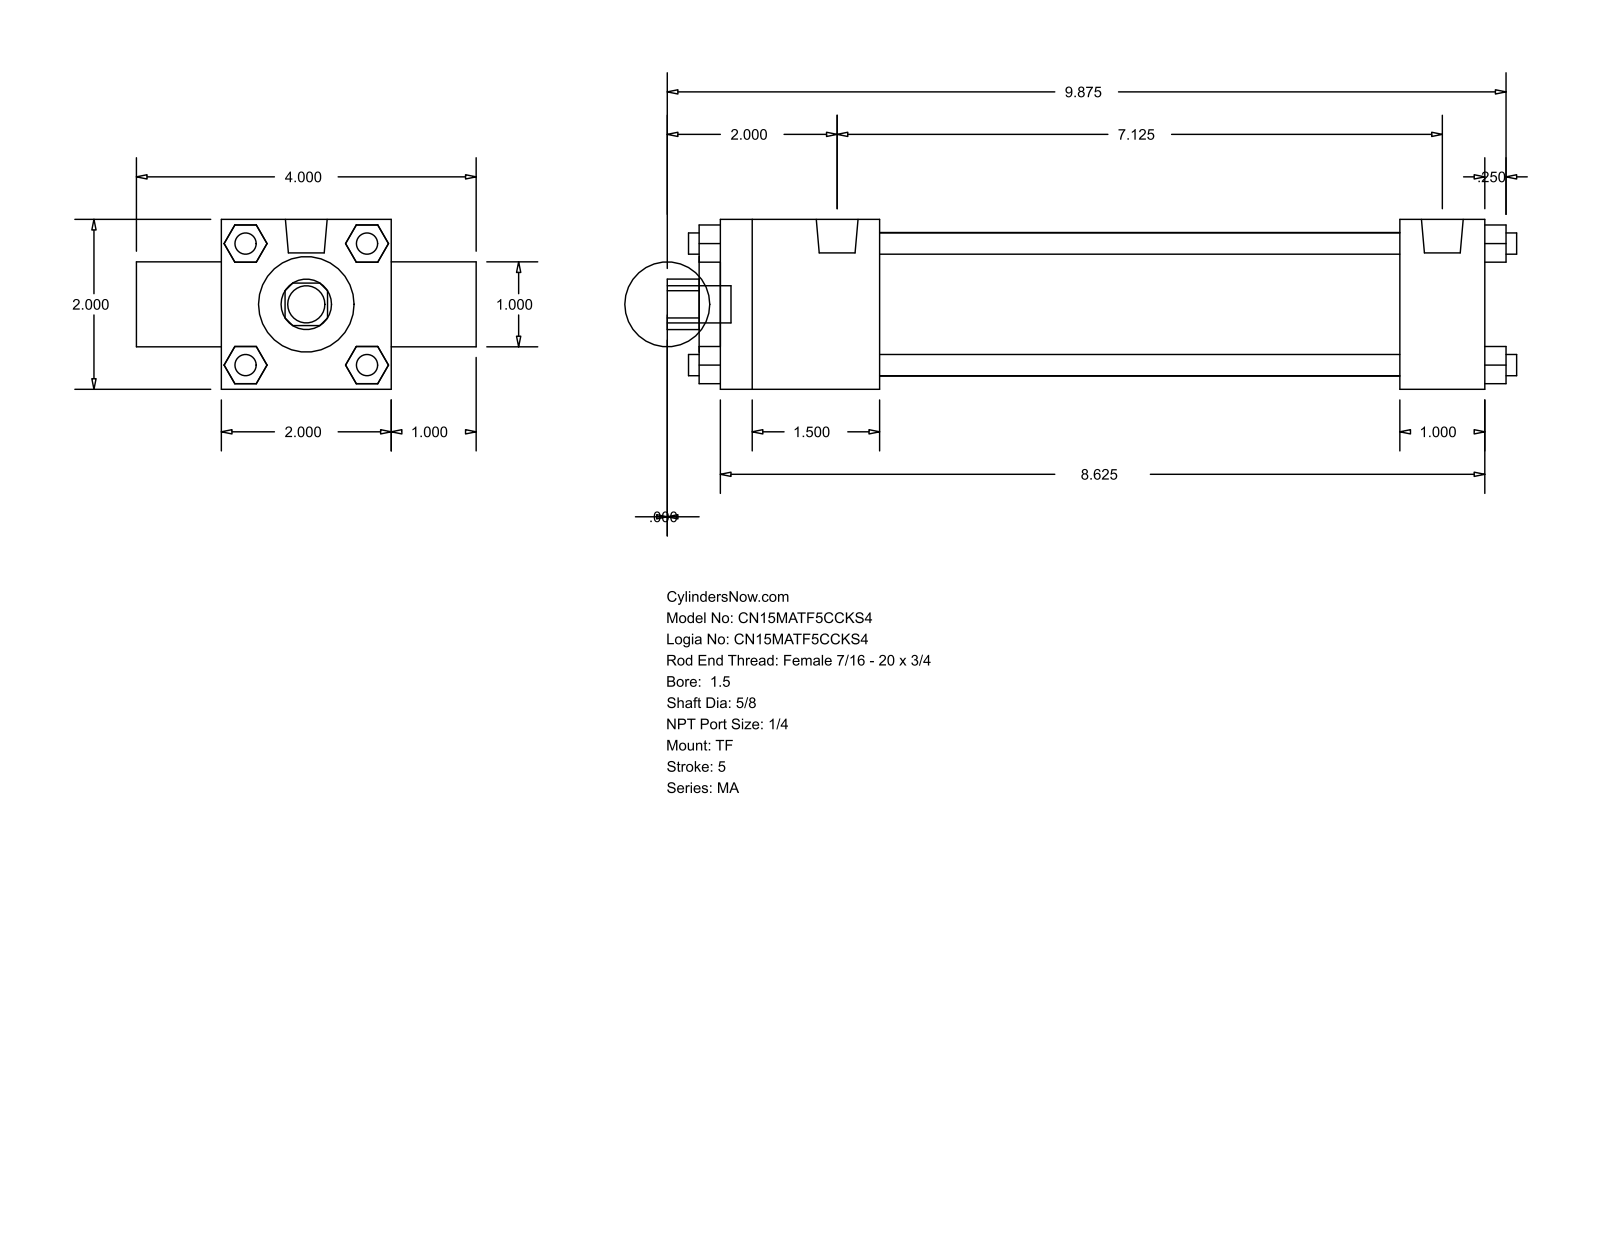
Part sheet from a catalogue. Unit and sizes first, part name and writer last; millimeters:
Units: millimetres
Overall size (bounding box): 254 × 101.6 × 50.8
Round holes (diameter × count): ⌀15.88 ×1, ⌀25.4 ×1, ⌀28.57 ×1, ⌀42.93 ×1
Round bosses / shafts (diameter × count): ⌀6.35 ×4, ⌀7.94 ×3, ⌀12.49 ×2, ⌀11.11 ×1
Partial cylindrical surfaces — rounded edges, fillets, slot ends (radius × count): R7.54 ×1
Main face-to-face distances: 50.8, 25.4, 228.59, 6.35, 234.94, 76.2, 47.62, 203.19, 155.57, 180.97
Bodies: 0 solids, 120 faces (92 planar, 28 cylindrical, 0 other)
Part name (STEP PRODUCT): MA_TF__0150_0.625
STEP written by: GSSL Pune (CONFIG_CONTROL_DESIGN)
